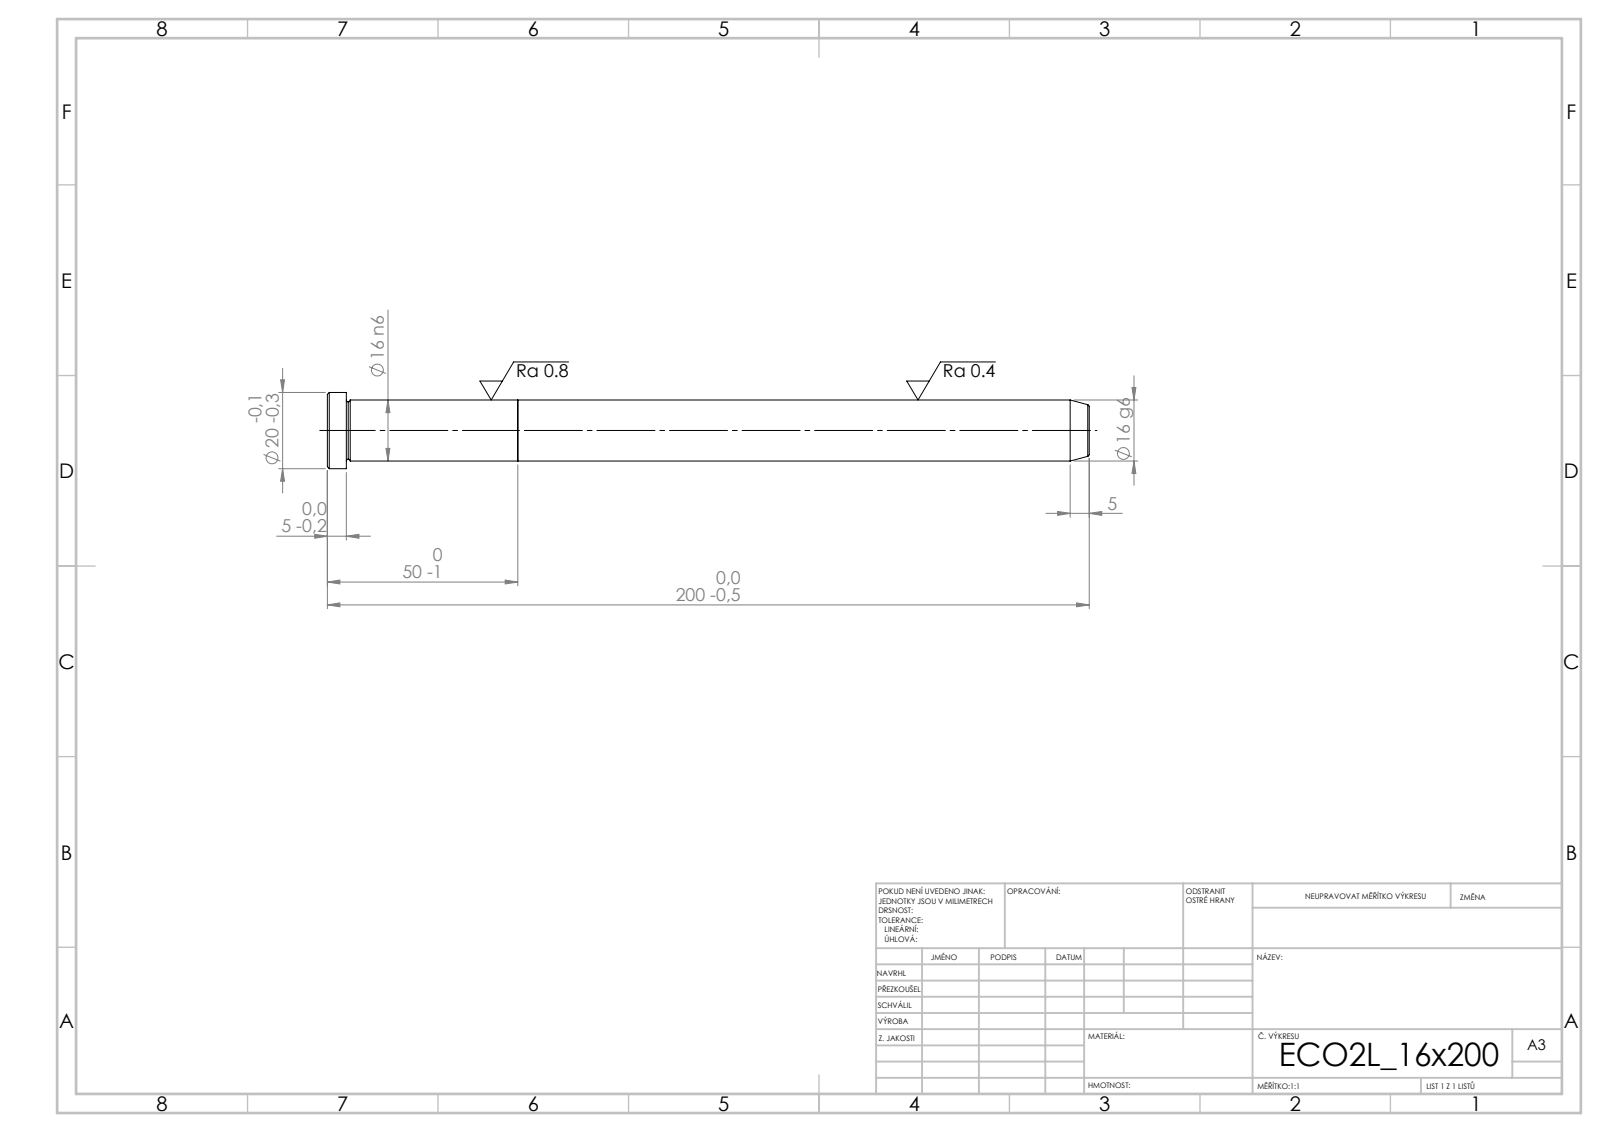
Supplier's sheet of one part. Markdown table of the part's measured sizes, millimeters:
| quantity | value |
| --- | --- |
| STEP written by | SolidWorks 2019 (CONFIG_CONTROL_DESIGN) |
| units | millimeters |
| bodies | 2 solids, 21 faces (5 planar, 6 cylindrical, 10 other) |
| overall size | 200 × 20 × 20 |
| volume | 40 591 mm³ |
| surface area | 11 074 mm² |
| round bosses / shafts (diameter × count) | 20 × 1, 16 × 1 |
| main face-to-face distances | 50, 150, 200, 195, 45, 5 |
